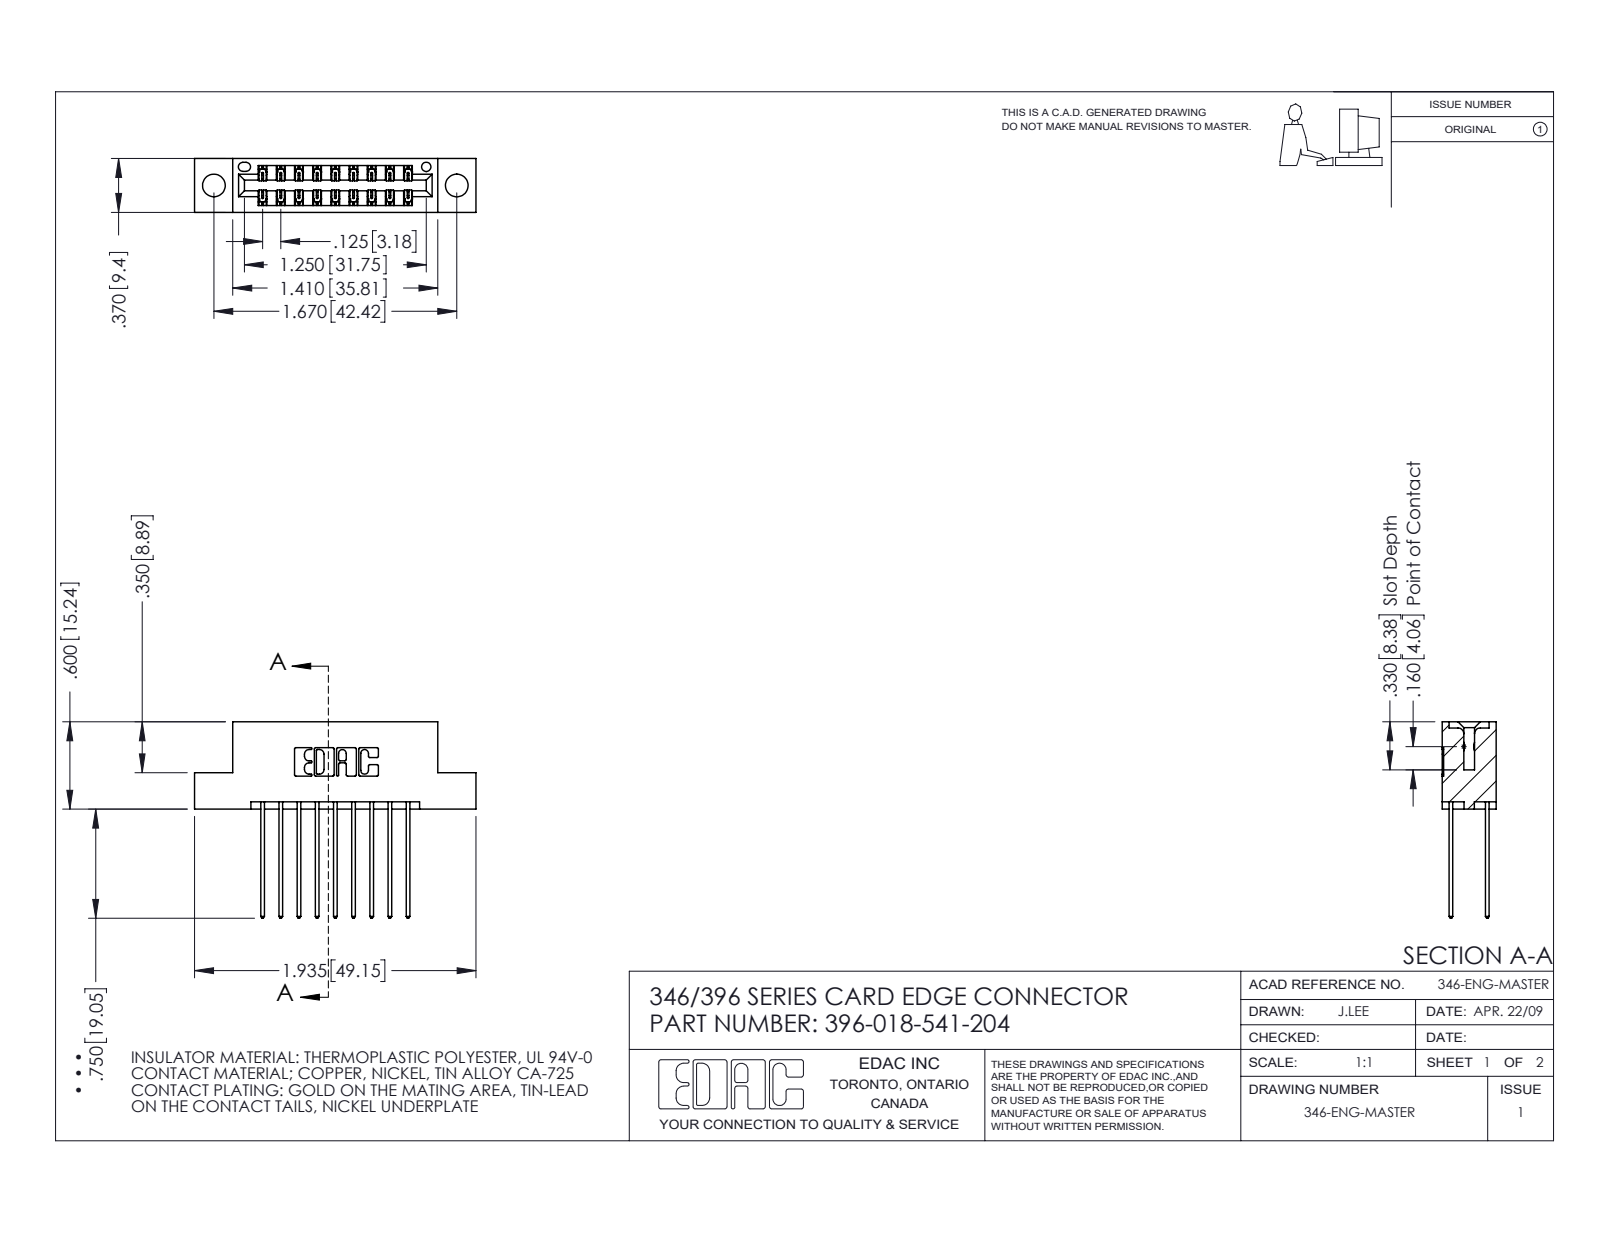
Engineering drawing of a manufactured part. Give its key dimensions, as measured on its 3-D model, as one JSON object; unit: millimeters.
{"part_name": "396-018-541-204; 346 Part_Flush Mounting Lugs - 0.156 Dia-TH; 345-292-001_345-293-141", "step_written_by": "SolidWorks 2016 (CONFIG_CONTROL_DESIGN)", "units": "millimeters", "bodies": {"solids": 19, "faces": 1058, "planar": 706, "cylindrical": 352, "other": 0}, "overall_size": [49.1, 34.3, 9.4], "volume_mm3": 4560, "surface_area_mm2": 6046, "round_holes": [[4, 2], [1.6, 1]], "partial_cylinders_radius": [[0.2, 27], [0.3, 22], [0.3, 18], [0.2, 6], [0.8, 6], [0.7, 3], [0.4, 2], [0.6, 2]], "face_to_face_distances": [6.4, 1.2, 8.2, 9.4, 1.8, 7.6, 0.6, 7, 3.8, 5.6], "hole_center_spacings": [6.2, 37.2, 42.4]}
